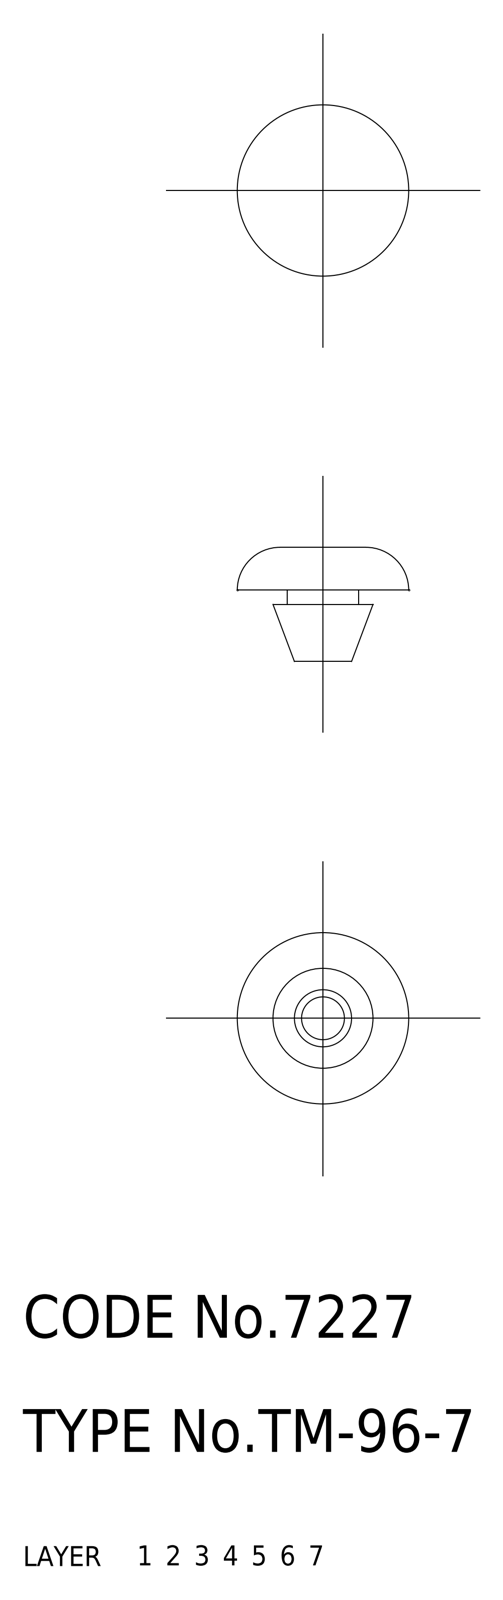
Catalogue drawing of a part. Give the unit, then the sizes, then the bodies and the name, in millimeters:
Units: millimetres
Overall size (bounding box): 12 × 12 × 8
Volume: 357 mm³ · Surface area: 435 mm²
Bodies: 1 solid, 13 faces (0 planar, 0 cylindrical, 13 other)
Part name (STEP PRODUCT): cushion
STEP written by: CADfix (AUTOMOTIVE_DESIGN)
